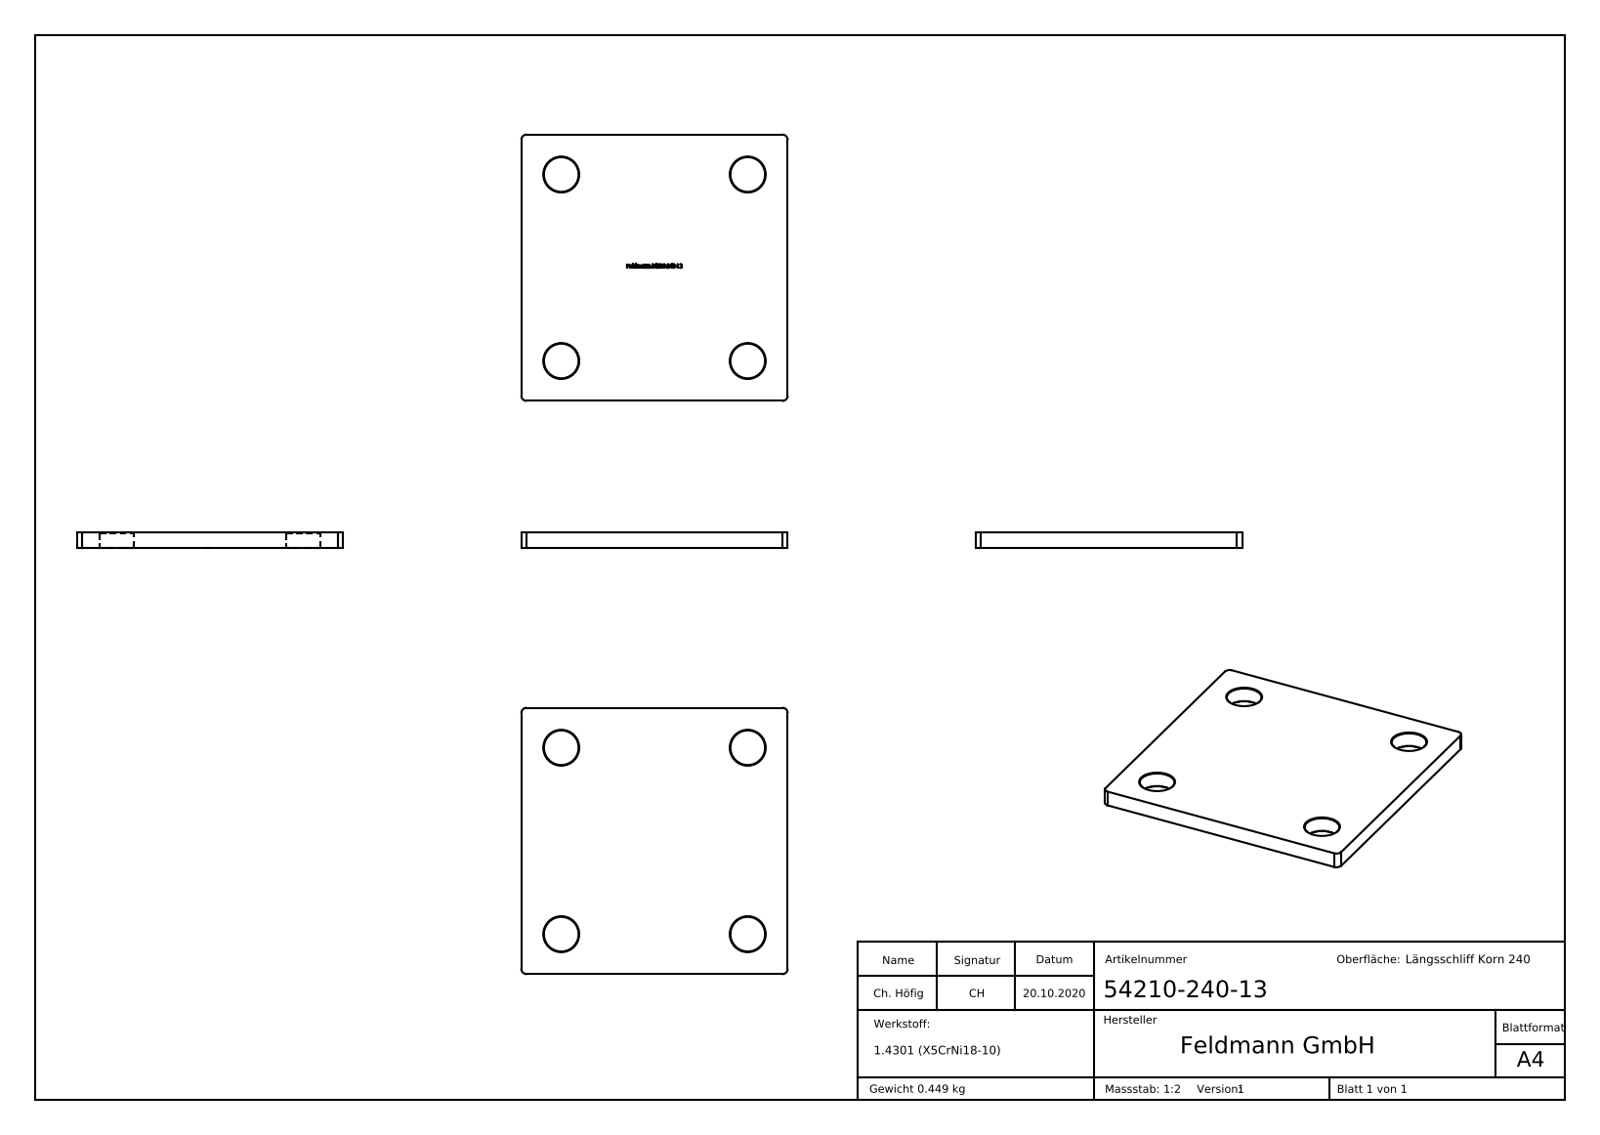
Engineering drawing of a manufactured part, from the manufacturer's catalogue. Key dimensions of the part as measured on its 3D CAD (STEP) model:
Part name (STEP PRODUCT): 54210-240-13
STEP written by: SolidWorks 2018 (CONFIG_CONTROL_DESIGN)
Units: millimetres
Bodies: 1 solid, 282 faces (154 planar, 12 cylindrical, 116 other)
Overall size (bounding box): 100 × 100 × 6
Volume: 56 783 mm³ · Surface area: 22 254 mm²
Round holes (diameter × count): ⌀13 ×4
Partial cylindrical surfaces — rounded edges, fillets, slot ends (radius × count): R2 ×4
Main face-to-face distances: 6, 100, 5.9, 50, 0.44, 0.88, 10.74, 17.05, 6.31, 2.02
Hole centre spacings: 70, 98.99
